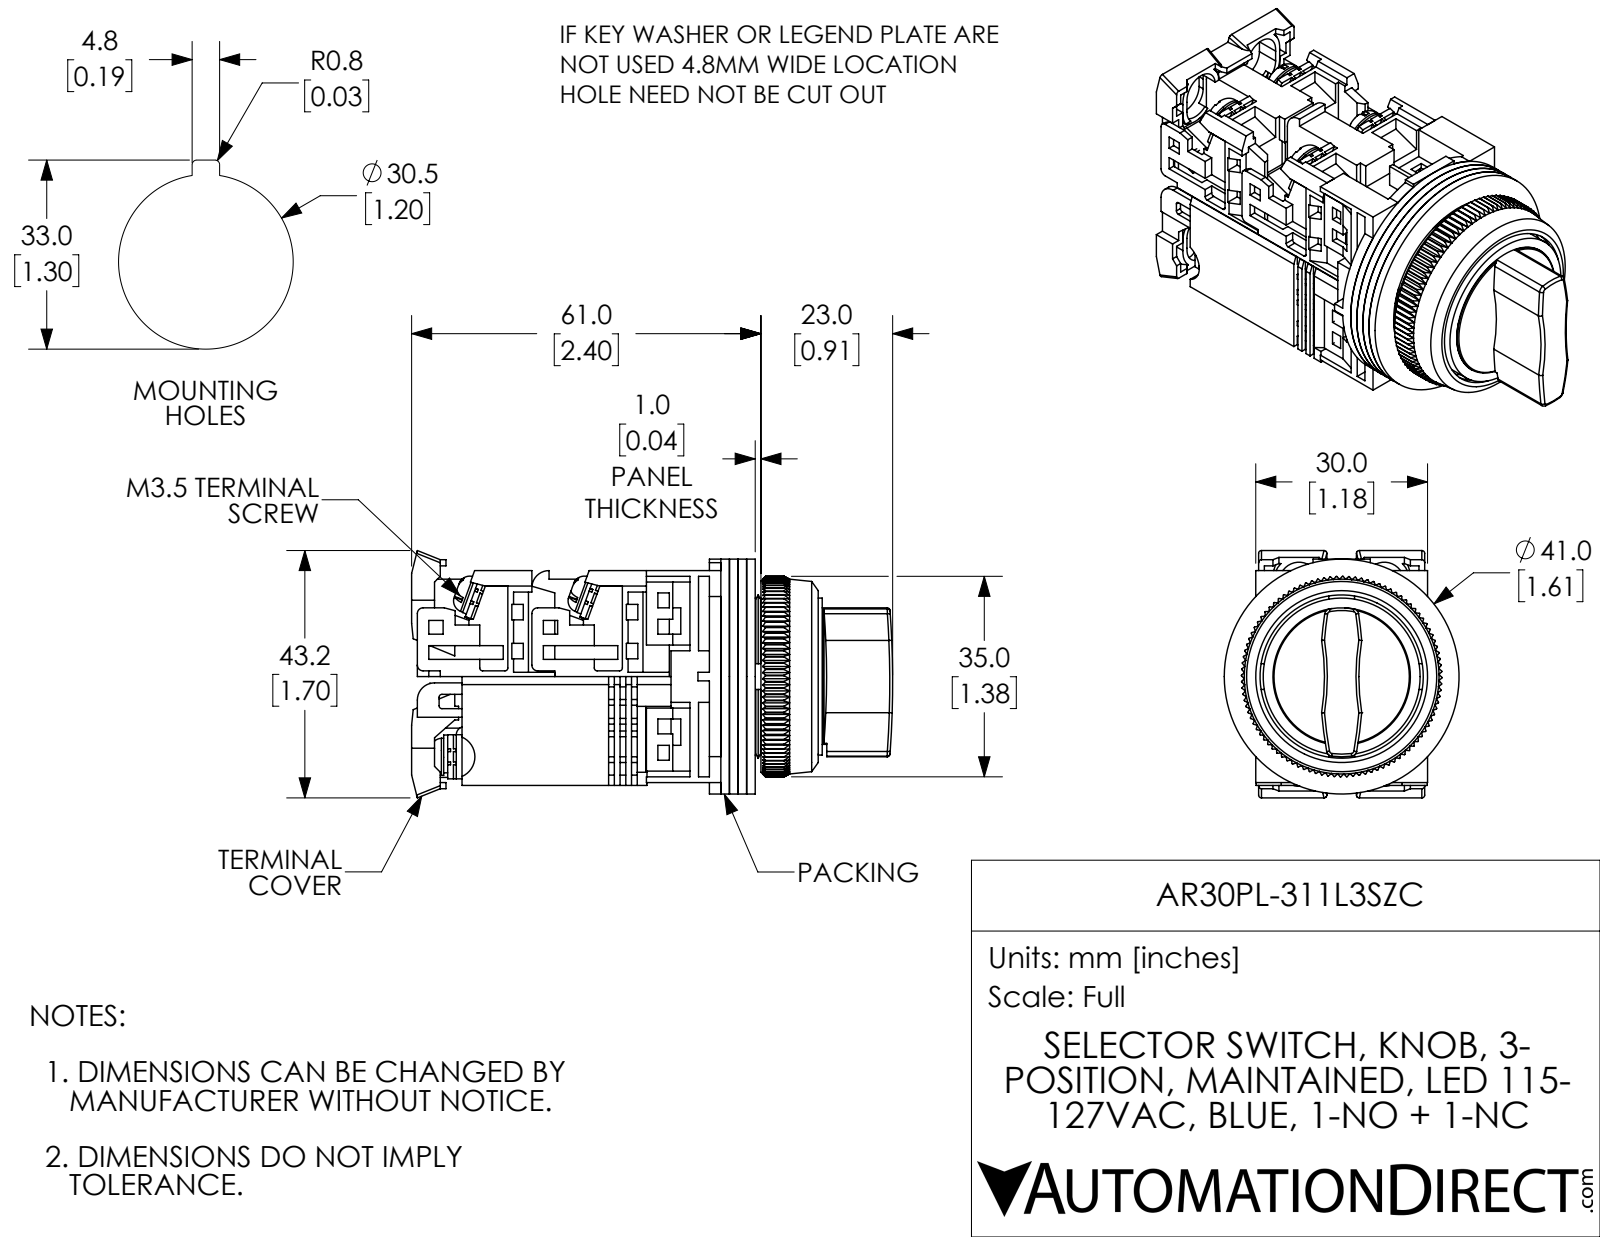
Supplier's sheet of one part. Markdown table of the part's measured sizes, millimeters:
| quantity | value |
| --- | --- |
| part name | AR30PL-311L3SZC |
| STEP written by | SolidWorks 2017 (AUTOMOTIVE_DESIGN) |
| units | millimeters |
| bodies | 34 solids, 2724 faces (2033 planar, 354 cylindrical, 337 other) |
| overall size | 84 × 43.2 × 41 |
| volume | 56 400 mm³ |
| surface area | 45 630 mm² |
| round holes (diameter × count) | 3.5 × 8, 3.6 × 6, 3 × 3, 12 × 1, 18 × 1, 19.5 × 1, 21 × 1, 28.5 × 1, 30 × 1, 31.8 × 1 |
| round bosses / shafts (diameter × count) | 6.6 × 6, 3.5 × 4, 1.6 × 2, 41 × 1, 29.2 × 1, 27.4 × 1, 24 × 1, 22.5 × 1 |
| partial cylindrical surfaces (radius × count) | 1.5 × 25, 0.5 × 15, 1 × 8, 3.5 × 4, 4.5 × 4, 3 × 3, 40 × 2, 75 × 2 |
| main face-to-face distances | 1.5, 3, 4.5, 1, 19, 2, 20, 1.6, 17.5, 5 |
| hole center spacings | 14.7, 6.8, 16.2, 7.5, 15.8, 0.5, 7.7, 14.8 |
